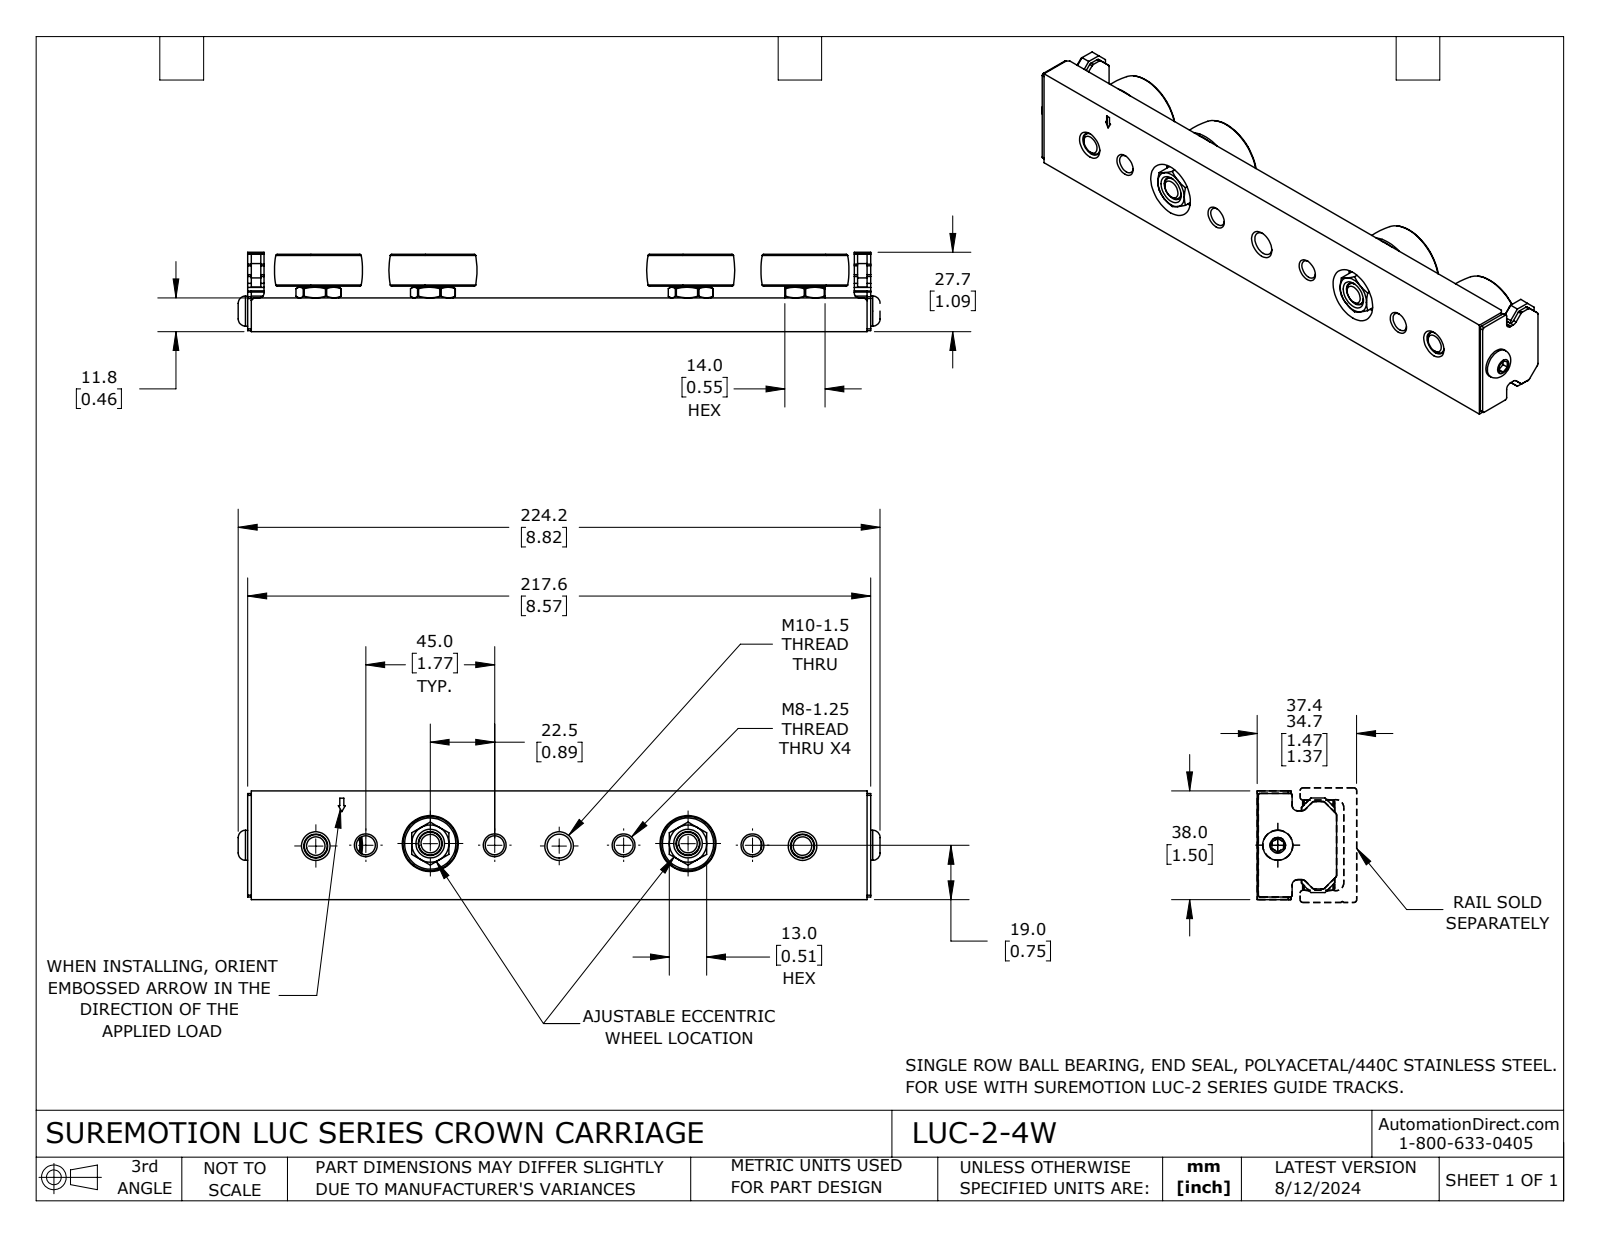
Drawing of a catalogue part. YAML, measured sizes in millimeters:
part_name: "LUC-2-4W"
step_written_by: "SolidWorks 2023 (CONFIG_CONTROL_DESIGN)"
units: millimeters
bodies: {solids: 9, faces: 658, planar: 264, cylindrical: 182, other: 212}
overall_size: [224.15, 38, 27.69]
volume: 128502
surface_area: 45425
round_holes:
  - {diameter: 8.38, count: 5}
  - {diameter: 6.65, count: 4}
  - {diameter: 19, count: 4}
  - {diameter: 9.59, count: 2}
  - {diameter: 19.56, count: 2}
  - {diameter: 4.92, count: 1}
  - {diameter: 4.92, count: 1}
round_bosses_or_shafts:
  - {diameter: 9.53, count: 4}
  - {diameter: 9.33, count: 4}
  - {diameter: 8, count: 4}
  - {diameter: 6.3, count: 4}
  - {diameter: 17.91, count: 1}
  - {diameter: 17.91, count: 1}
  - {diameter: 10.5, count: 1}
  - {diameter: 6, count: 1}
partial_cylinders:
  - {radius: 0.64, count: 12}
  - {radius: 0.38, count: 6}
  - {radius: 0.84, count: 6}
  - {radius: 1.98, count: 4}
  - {radius: 7.95, count: 4}
  - {radius: 1.78, count: 2}
face_to_face_distances: [11.79, 38, 1.86, 9.27, 1.27, 216.29, 4.06, 26.98, 15.19, 15.85]
hole_center_spacings: [0.97, 22.51, 45.01, 90.02, 22.52, 39.99, 45.02, 67.51]
